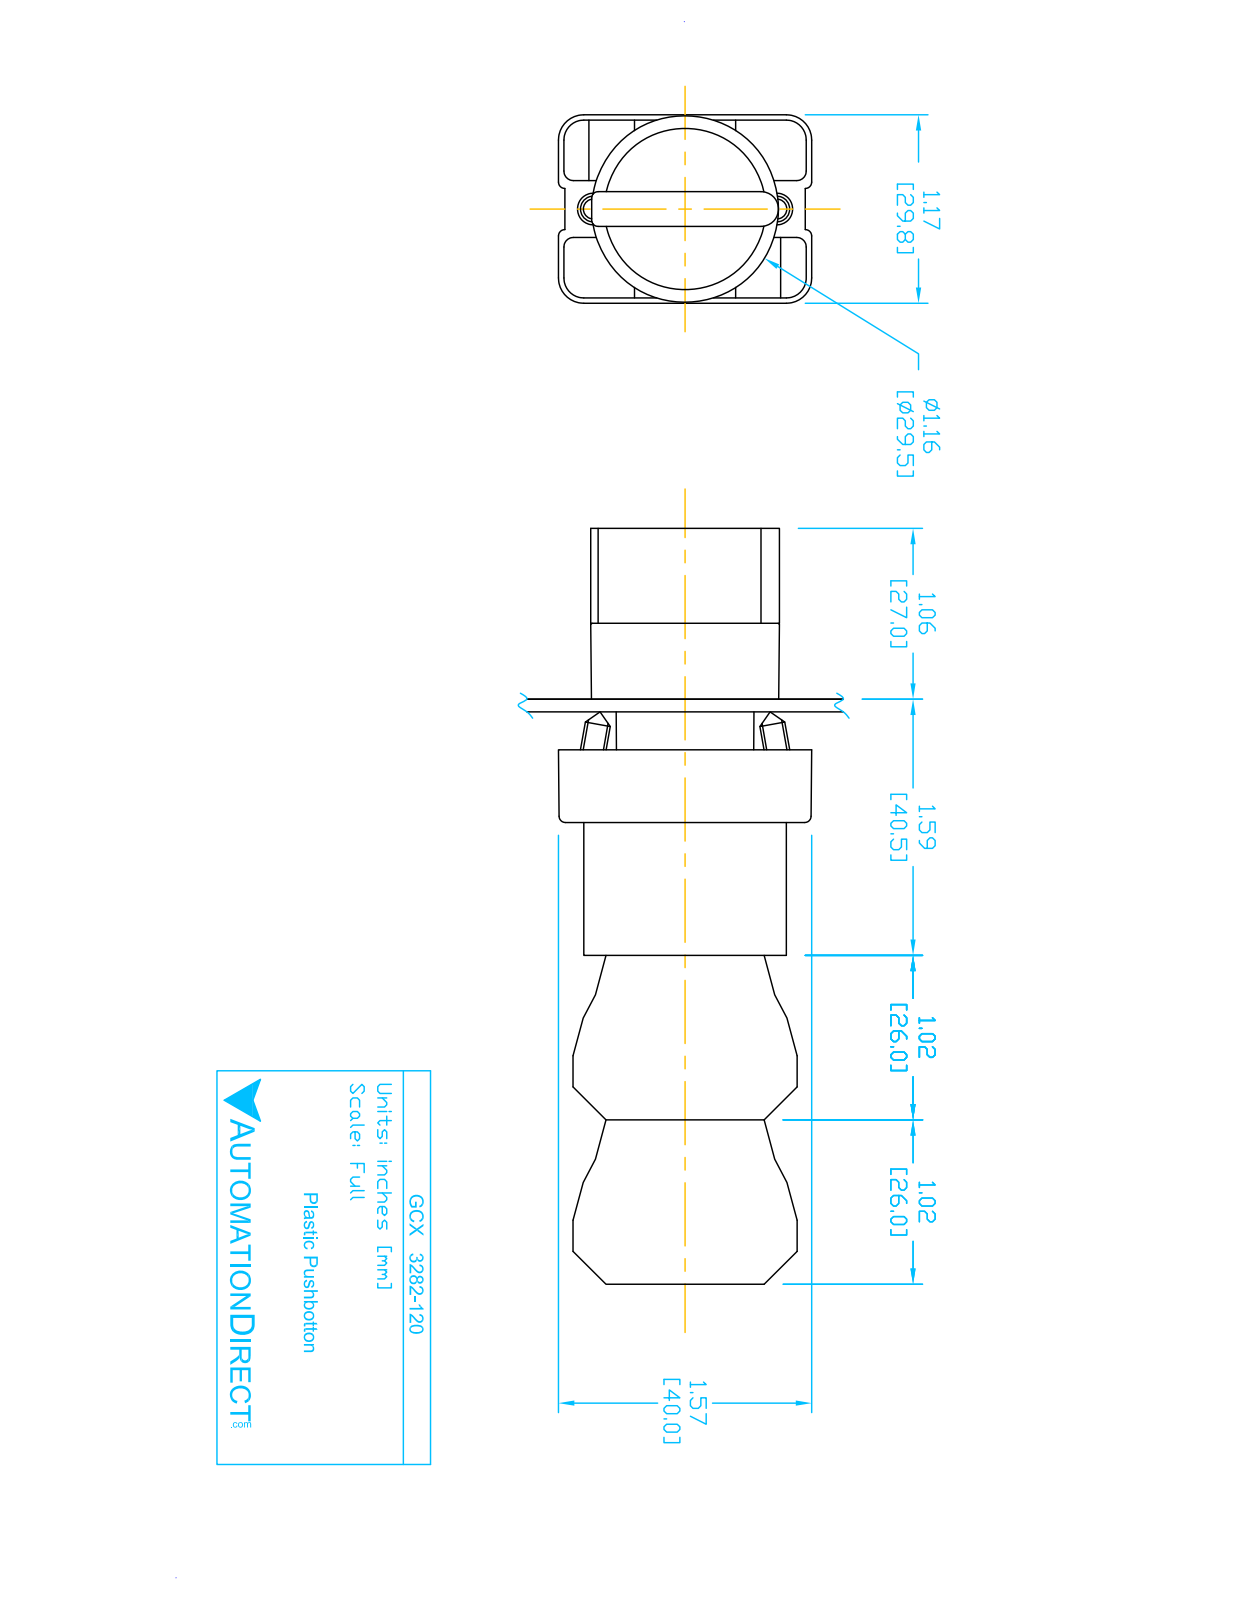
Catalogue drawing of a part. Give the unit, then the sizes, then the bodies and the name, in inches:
Units: inches
Overall size (bounding box): 4.677 × 1.581 × 1.177
Round holes (diameter × count): ⌀0.079 ×4, ⌀0.087 ×2, ⌀0.124 ×2, ⌀0.13 ×2, ⌀0.197 ×1, ⌀0.469 ×1, ⌀0.878 ×1, ⌀0.888 ×1, ⌀1.024 ×1
Round bosses / shafts (diameter × count): ⌀0.157 ×4, ⌀1.175 ×1, ⌀1.004 ×1, ⌀0.945 ×1, ⌀0.856 ×1, ⌀0.78 ×1, ⌀0.504 ×1
Partial cylindrical surfaces — rounded edges, fillets, slot ends (radius × count): R0.059 ×24, R0.041 ×12, R0.124 ×12, R0.157 ×12, R0.039 ×9, R0.02 ×2, R0.063 ×2, R0.079 ×2
Main face-to-face distances: 0.579, 0.593, 1.024, 1.171, 0.014, 0.827, 1.85, 3.043, 2.02, 1.193
Hole centre spacings: 0.236, 1.003, 0.974, 0.472, 0.539, 0.544, 1.083, 0.484
Volume: 4.751 in³ · Surface area: 59.22 in²
Bodies: 11 solids, 724 faces (488 planar, 193 cylindrical, 43 other)
Part name (STEP PRODUCT): GCX3282 OPERATOR; ECX1050; ecx1030; ecx1040 (+2 more)
STEP written by: SolidWorks 2016 (AUTOMOTIVE_DESIGN)
